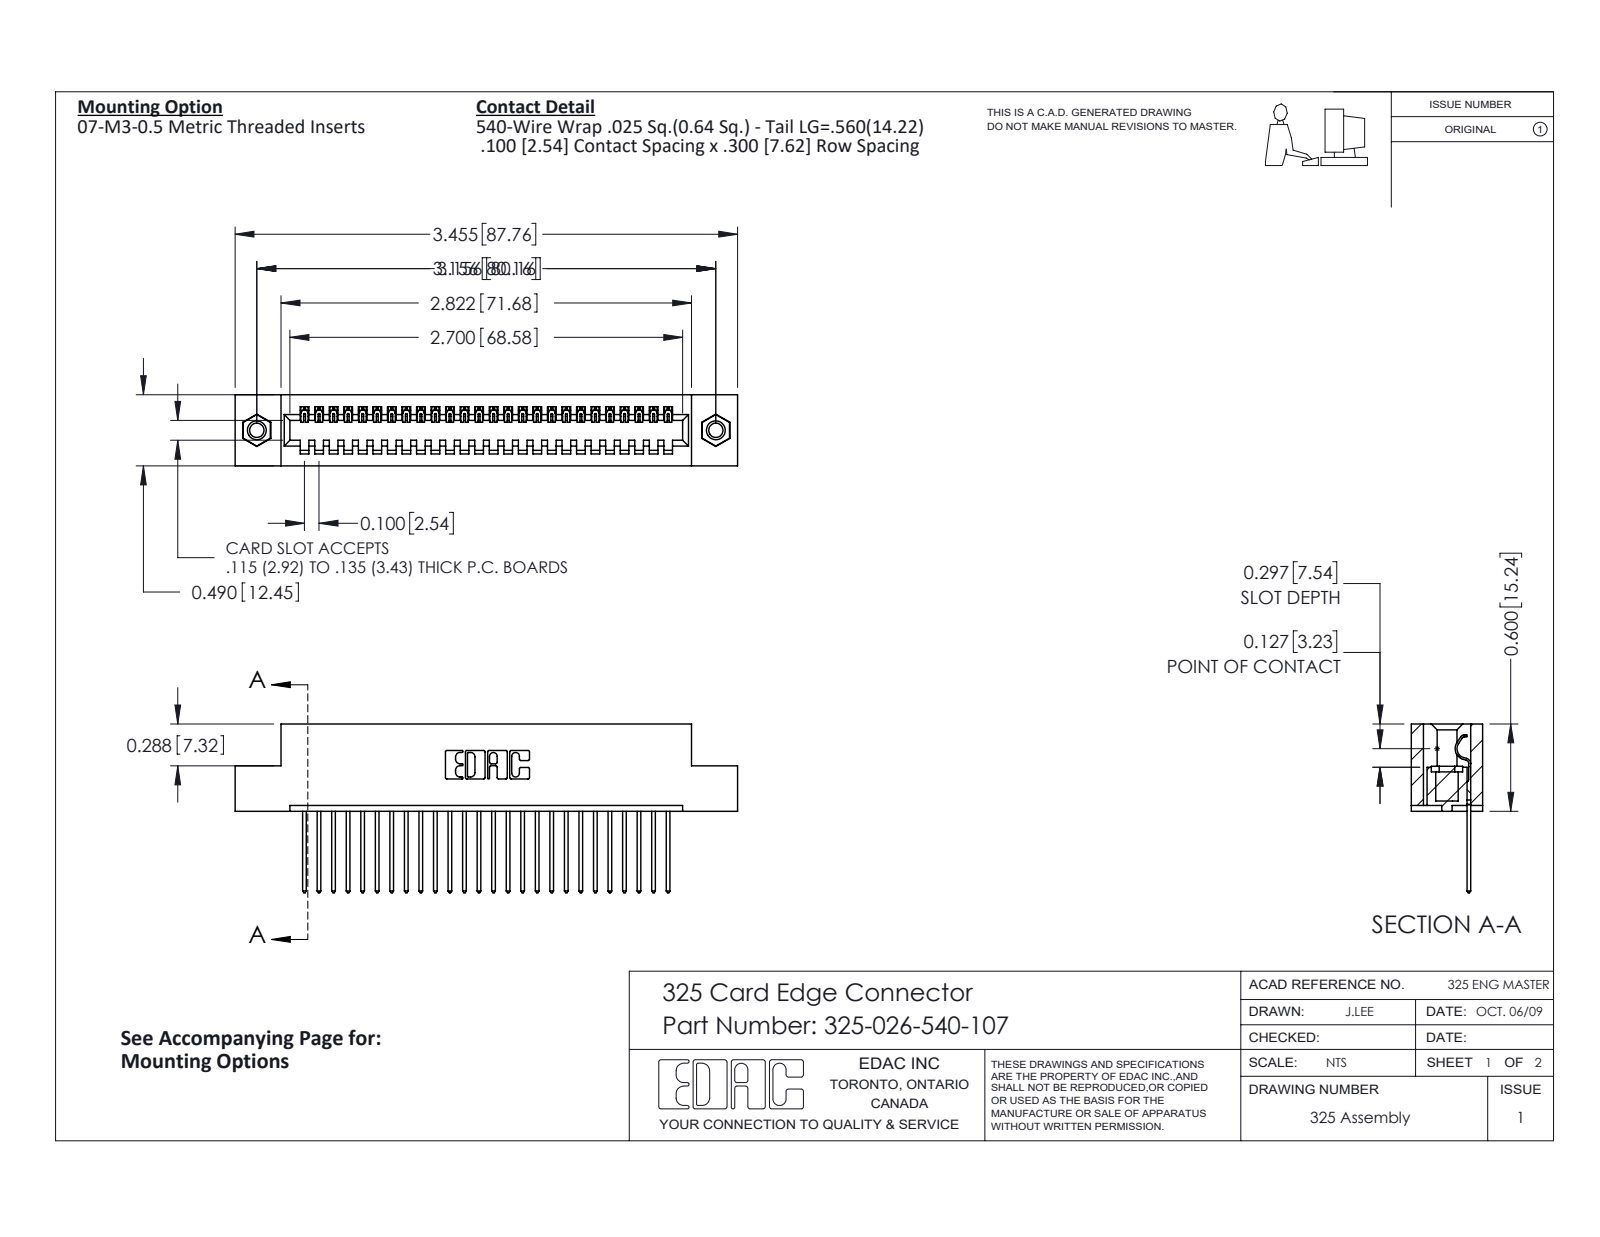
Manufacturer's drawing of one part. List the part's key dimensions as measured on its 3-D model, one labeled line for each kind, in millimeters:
Part name (STEP PRODUCT): 325 Part_TI; 325-292-001_325-293-140; 325-026-540-107; 345-250-001_345-250-005-103
STEP written by: SolidWorks 2016 (CONFIG_CONTROL_DESIGN)
Units: millimetres
Bodies: 29 solids, 1682 faces (1194 planar, 472 cylindrical, 16 other)
Overall size (bounding box): 87.8 × 29.5 × 12.4
Volume: 11 000 mm³ · Surface area: 12 070 mm²
Round holes (diameter × count): ⌀2.5 ×2, ⌀3.2 ×2, ⌀4.1 ×2
Round bosses / shafts (diameter × count): ⌀3.9 ×2
Partial cylindrical surfaces — rounded edges, fillets, slot ends (radius × count): R0.2 ×52, R0.3 ×52, R0.3 ×22, R0.2 ×6, R0.8 ×6, R0.7 ×3, R0.4 ×1, R0.6 ×1
Main face-to-face distances: 2.1, 10.3, 12.4, 7.6, 2.7, 9.7, 0.6, 8.3, 1, 15.2
Hole centre spacings: 80.2
